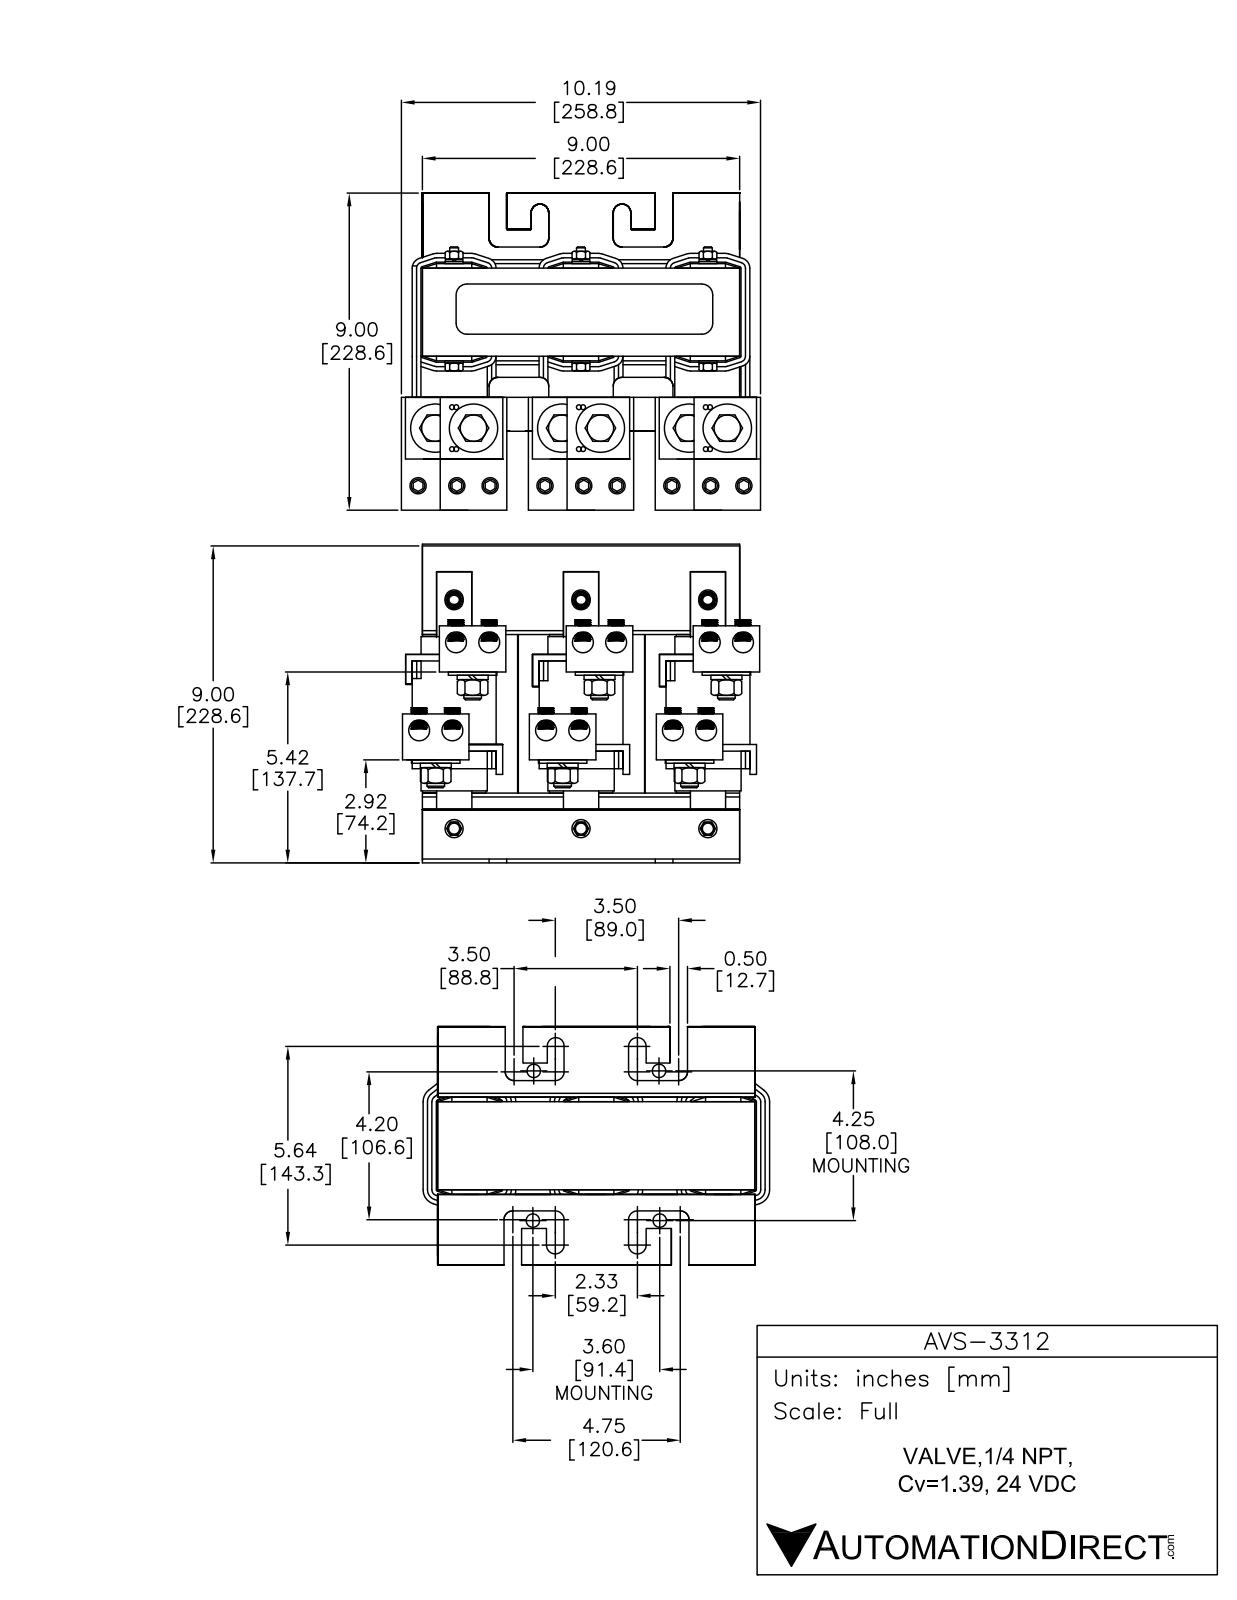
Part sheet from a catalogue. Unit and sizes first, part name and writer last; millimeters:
Units: millimetres
Overall size (bounding box): 285.26 × 253.32 × 213.6
Round holes (diameter × count): ⌀15.5 ×12, ⌀19 ×12
Round bosses / shafts (diameter × count): ⌀35 ×12, ⌀15.5 ×9, ⌀19.75 ×6, ⌀14.5 ×6, ⌀12.25 ×6, ⌀6.25 ×3
Partial cylindrical surfaces — rounded edges, fillets, slot ends (radius × count): R1 ×80, R20.33 ×48, R16.34 ×30, R119.94 ×27, R4.16 ×21, R4.37 ×21, R7.73 ×21, R7.94 ×21
Main face-to-face distances: 3, 91.75, 63.5, 66.5, 46, 69.5, 183.5, 29.62, 89.62, 75.62
Hole centre spacings: 91.75, 25, 66.75, 116.75, 183.5, 4.53, 74.72, 87.27
Volume: 5 239 000 mm³ · Surface area: 932 101 mm²
Bodies: 57 solids, 1973 faces (1066 planar, 883 cylindrical, 24 other)
Part name (STEP PRODUCT): LR-4250
STEP written by: SolidWorks 2011 (AUTOMOTIVE_DESIGN)
